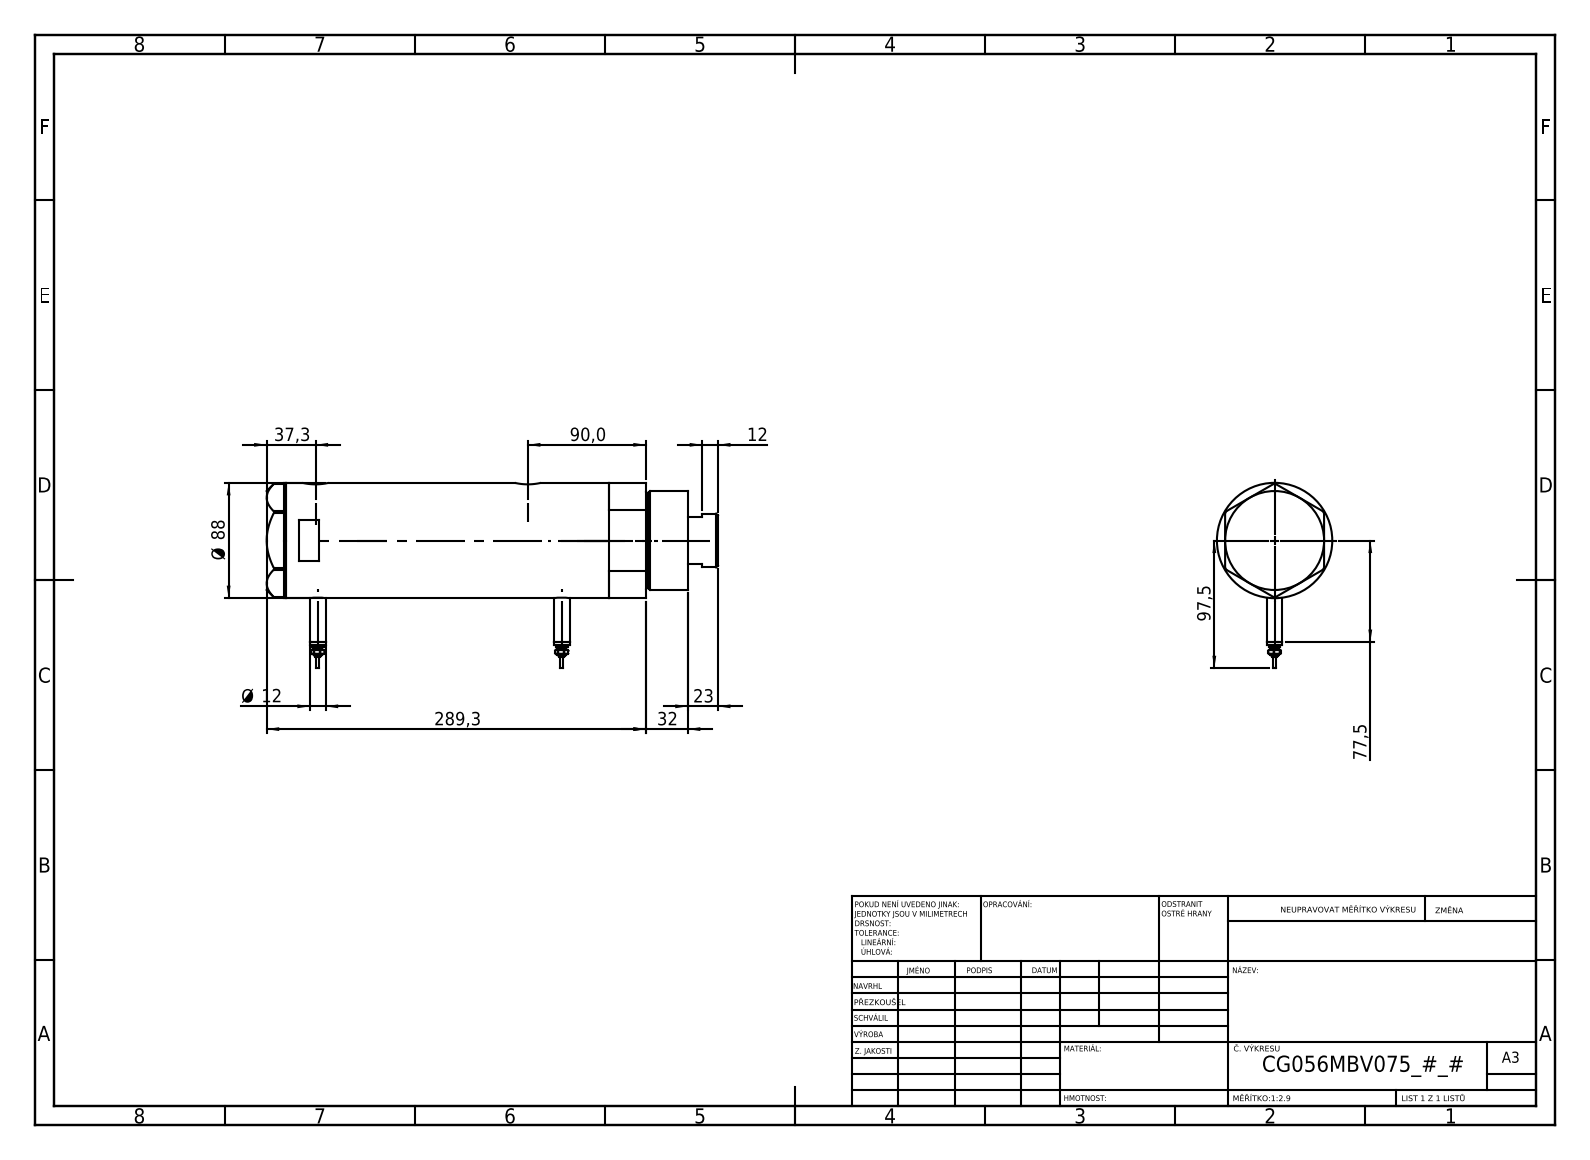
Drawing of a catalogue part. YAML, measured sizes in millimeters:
part_name: "V270CG_VC; V270CG_BACK; Switch; V270CG_FRONT (+1 more)"
step_written_by: "SolidWorks 2019 (CONFIG_CONTROL_DESIGN)"
units: millimeters
bodies: {solids: 6, faces: 213, planar: 80, cylindrical: 69, other: 64}
overall_size: [344.3, 141.5, 88]
volume: 1818000
surface_area: 254906
round_holes:
  - {diameter: 12.5, count: 2}
  - {diameter: 13.16, count: 2}
  - {diameter: 20, count: 2}
  - {diameter: 14.5, count: 1}
  - {diameter: 42, count: 1}
  - {diameter: 43.5, count: 1}
  - {diameter: 56, count: 1}
  - {diameter: 60, count: 1}
  - {diameter: 80, count: 1}
round_bosses_or_shafts:
  - {diameter: 12, count: 2}
  - {diameter: 9, count: 2}
  - {diameter: 7, count: 2}
  - {diameter: 4.5, count: 2}
  - {diameter: 2.5, count: 2}
  - {diameter: 88, count: 1}
  - {diameter: 75, count: 1}
  - {diameter: 73, count: 1}
face_to_face_distances: [184.4, 26, 158.4, 15, 41, 199.4, 306.3, 321.3, 280.3, 121.9]
hole_center_spacings: [1.7, 25.8, 160.3, 162, 186.1, 187.8]
